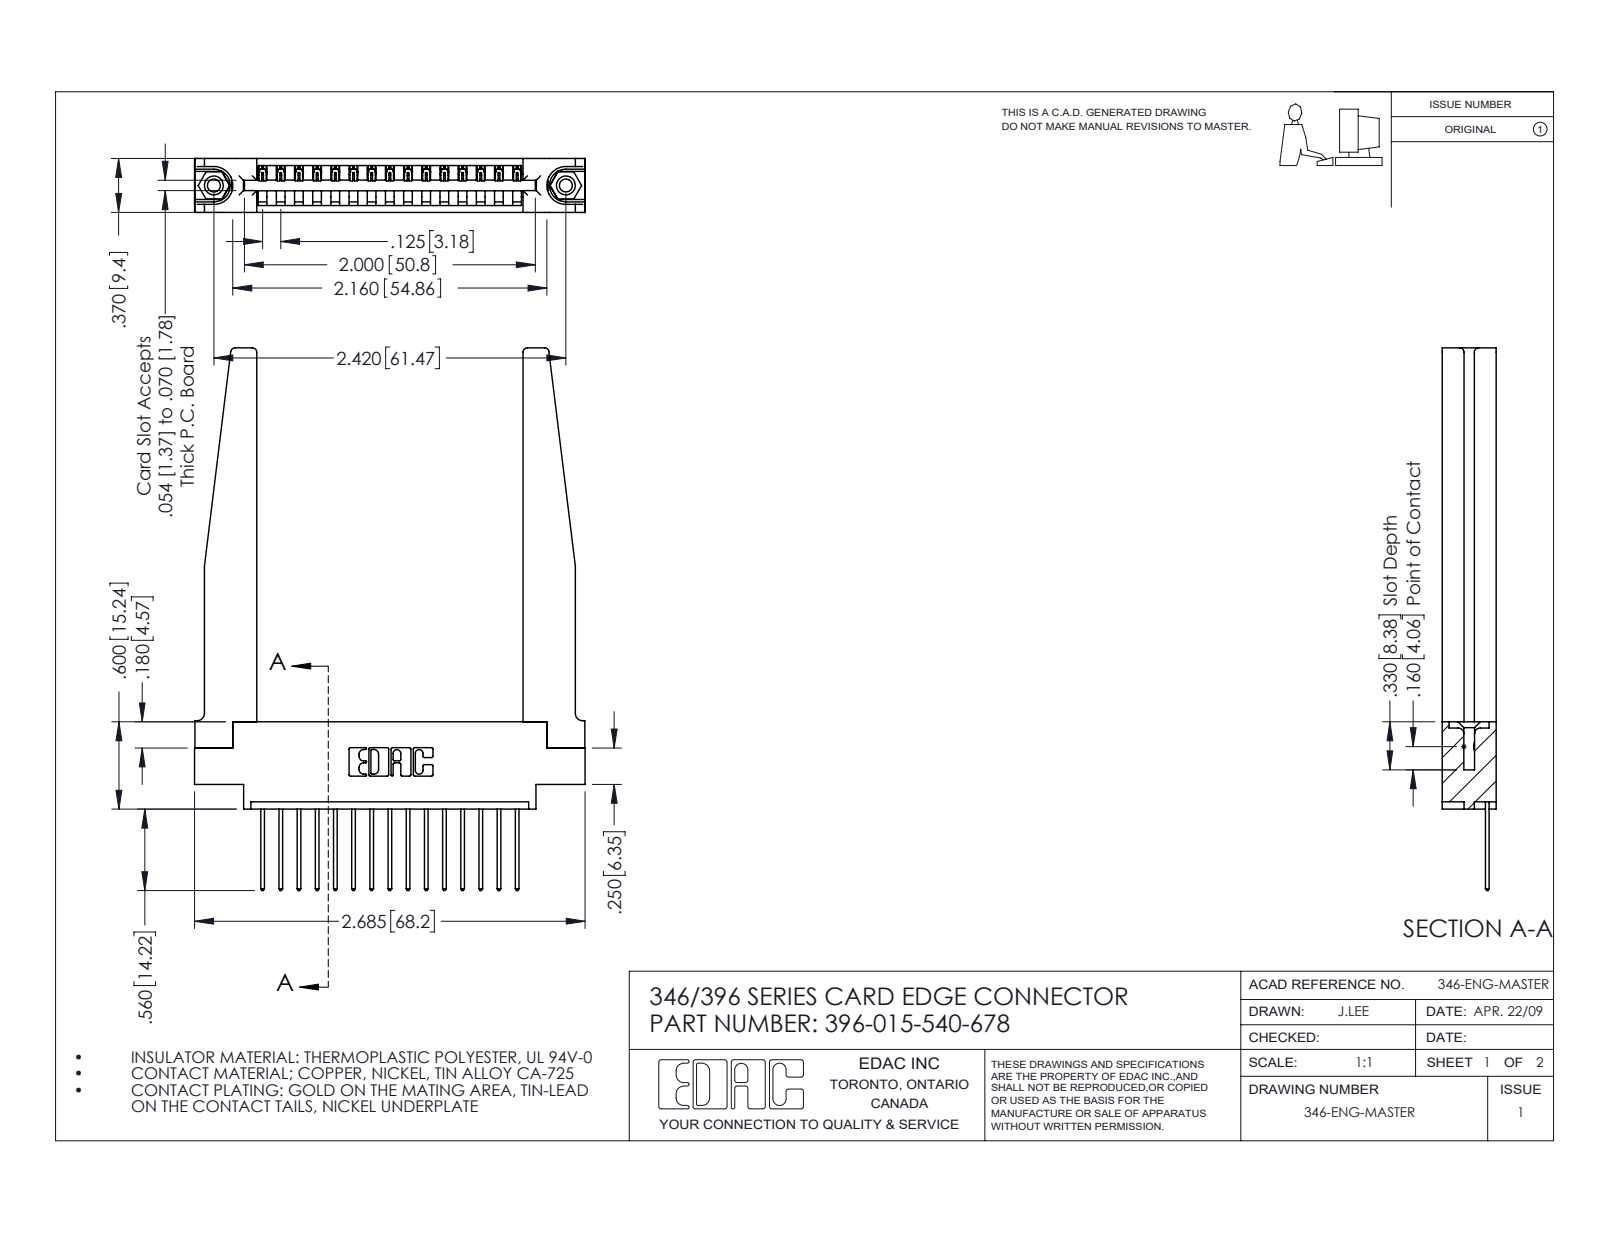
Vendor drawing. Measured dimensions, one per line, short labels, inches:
name: 345-292-001_345-293-140; 345-250-001_345-250-001-102; 396-015-540-678; 346 Part_0.170 Offset - 0.156 Dia-TH (+1 more)
written by: SolidWorks 2016 (CONFIG_CONTROL_DESIGN)
unit: in
bodies: 20 solids, 1230 faces (822 planar, 356 cylindrical, 52 other)
size: 3.73 × 2.685 × 0.37
volume: 0.8 in³; area: 22.19 in²
holes: 2× ⌀0.089, 2× ⌀0.125, 2× ⌀0.156, 1× ⌀0.064
bosses: 2× ⌀0.155
rounds: 30× R0.006, 30× R0.01, 22× R0.01, 8× R0.03, 6× R0.007, 6× R0.031, 3× R0.026, 2× R0.031
face distances: 0.37, 0.072, 0.15, 0.048, 0.322, 0.148, 0.25, 0.102, 0.22, 0.173
hole spacings: 0.246, 2.213, 2.42
